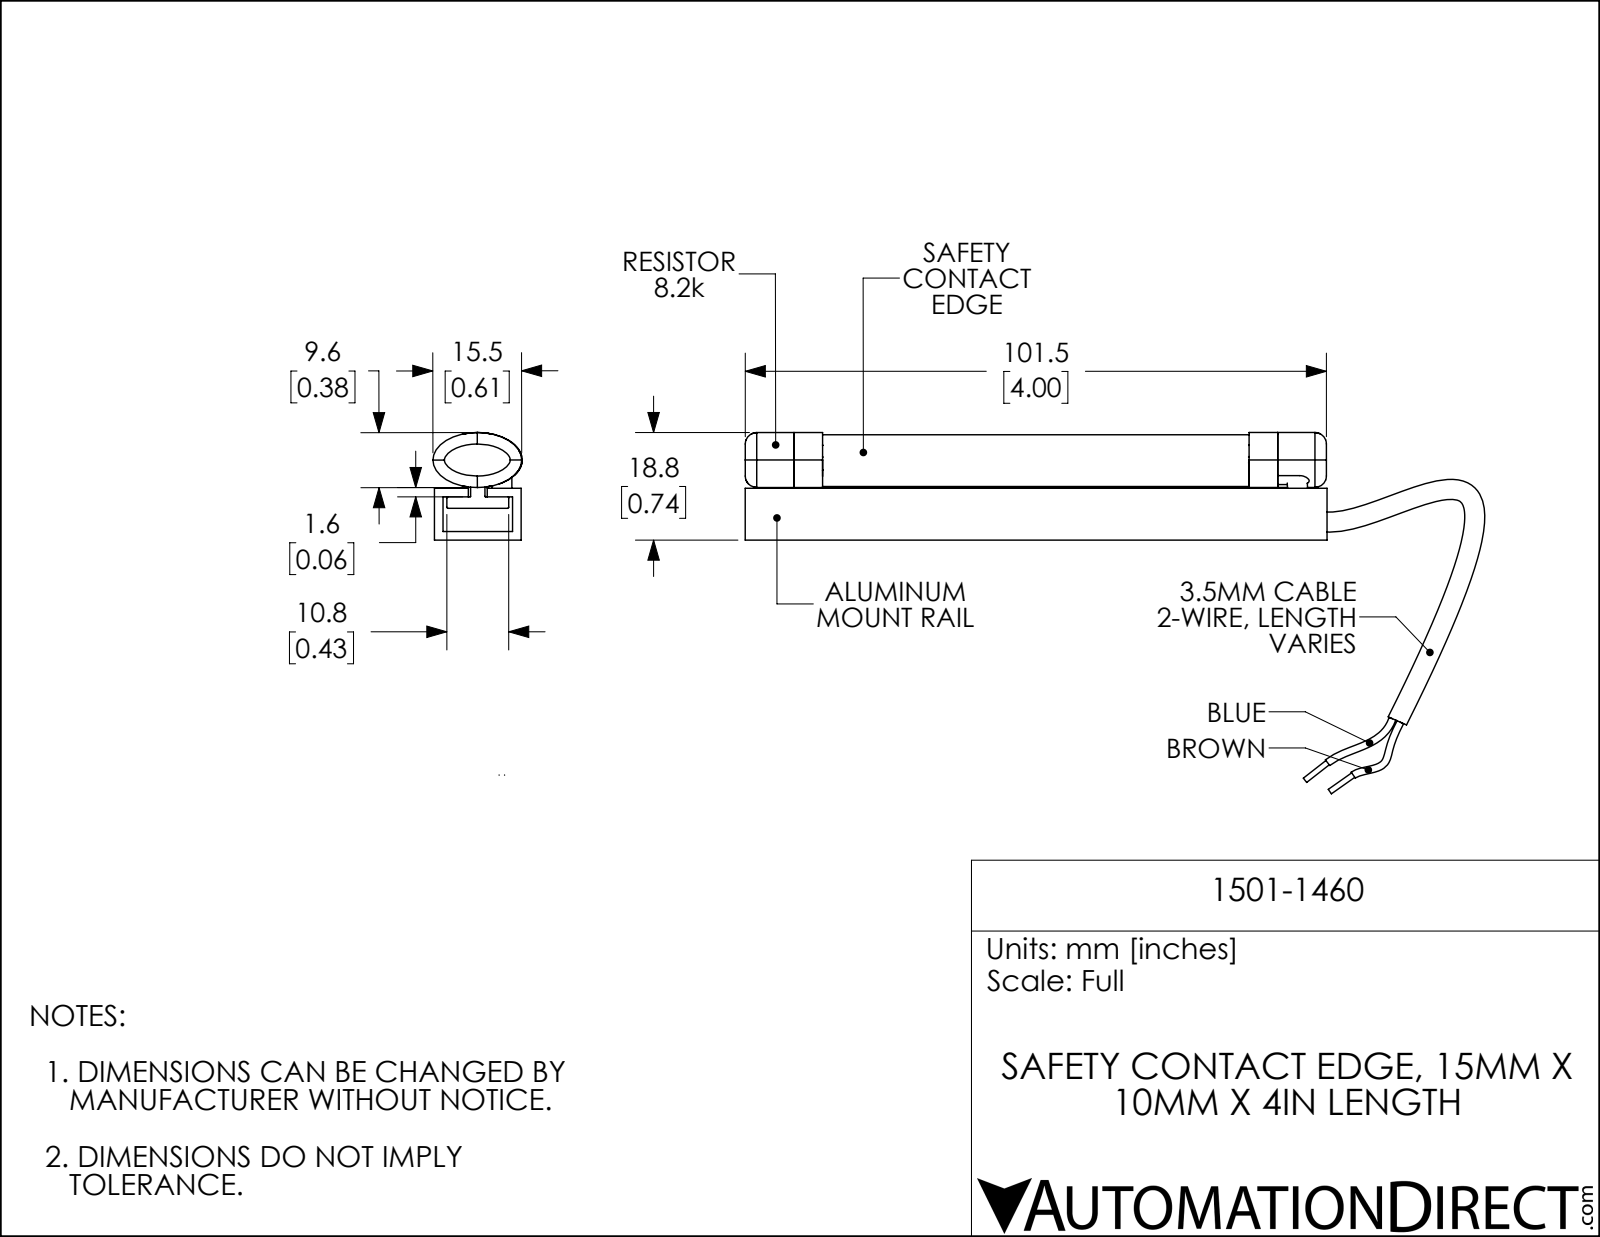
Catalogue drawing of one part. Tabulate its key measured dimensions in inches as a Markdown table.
| quantity | value |
| --- | --- |
| part name | 1501-1460 |
| STEP written by | SolidWorks 2018 (AUTOMOTIVE_DESIGN) |
| units | inches |
| bodies | 7 solids, 607 faces (129 planar, 154 cylindrical, 324 other) |
| overall size | 5.084 × 2.483 × 0.613 |
| volume | 1.039 in³ |
| surface area | 31.11 in² |
| round holes (diameter × count) | 0.047 × 4 |
| round bosses / shafts (diameter × count) | 0.037 × 2 |
| partial cylindrical surfaces (radius × count) | 0.004 × 56, 0.016 × 14, 0.012 × 10, 0.008 × 7, 0.02 × 4, 0.059 × 4, 0.098 × 4, 0.512 × 4 |
| main face-to-face distances | 0.059, 0.297, 0.238, 0.537, 0.356, 0.596, 0.079, 0.138, 0.219, 0.159 |
| hole center spacings | 0.197, 0.194, 0.2 |
